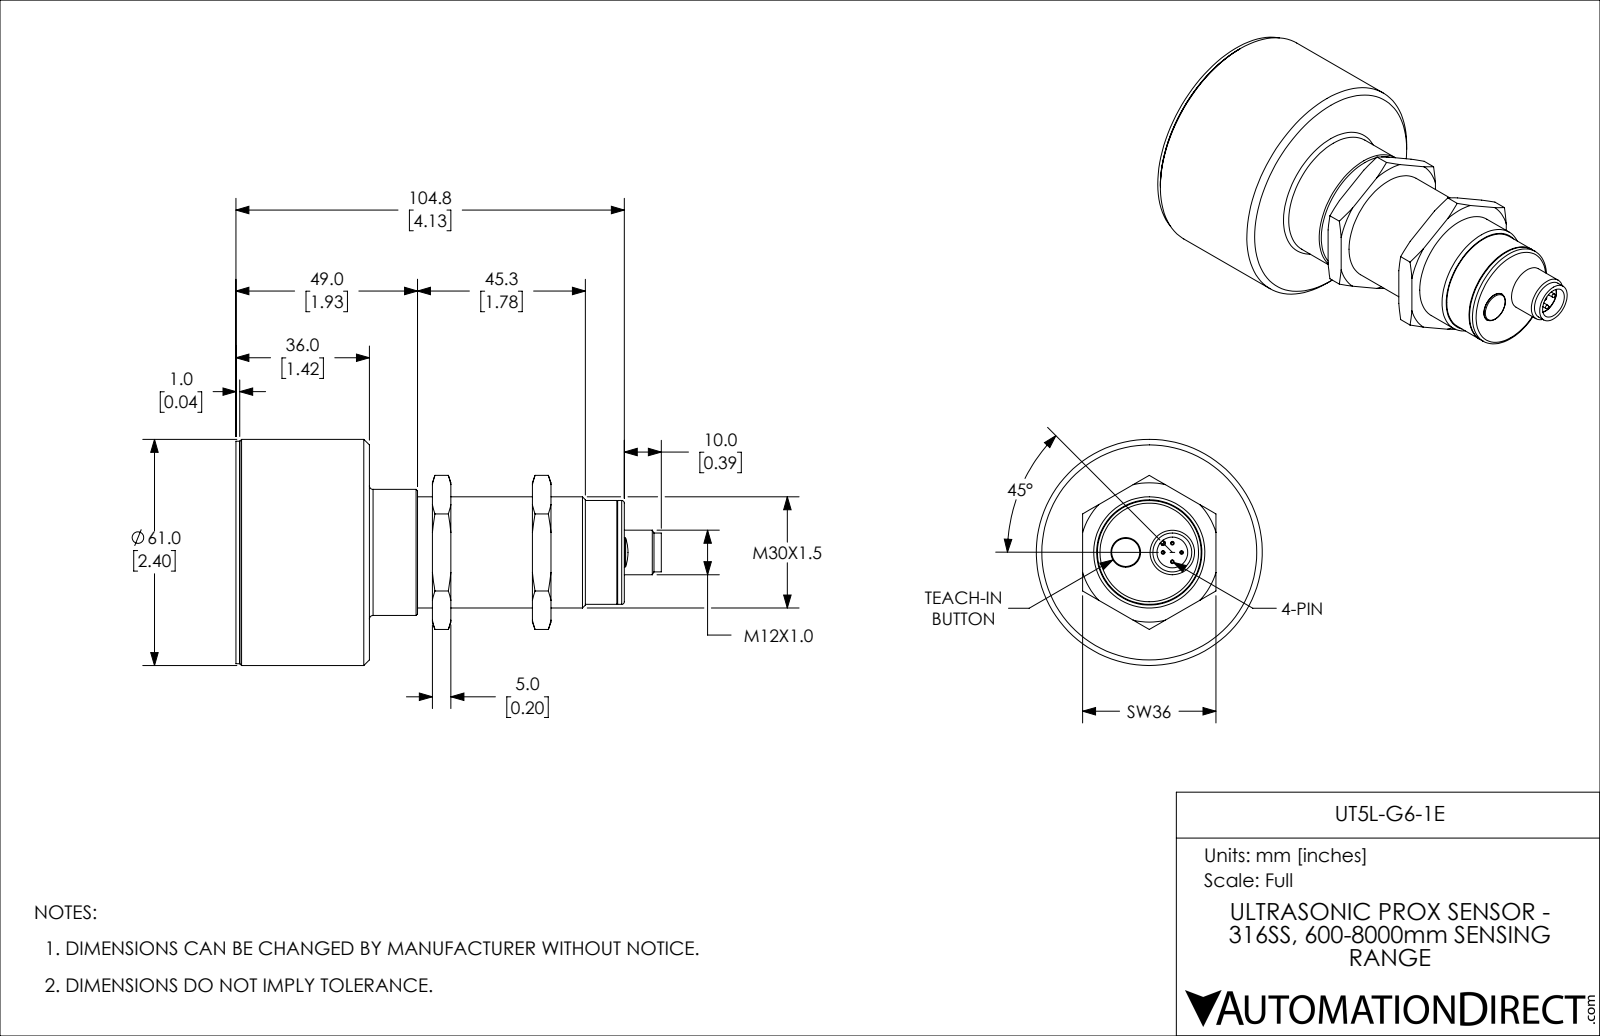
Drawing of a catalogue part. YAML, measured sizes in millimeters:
part_name: "UT5L-G6-1E"
step_written_by: "SolidWorks 2018 (AUTOMOTIVE_DESIGN)"
units: millimeters
bodies: {solids: 9, faces: 180, planar: 52, cylindrical: 57, other: 71}
overall_size: [114.8, 61, 61]
volume: 194457
surface_area: 35986
round_holes:
  - {diameter: 1.8, count: 4}
  - {diameter: 8, count: 1}
  - {diameter: 8.3, count: 1}
  - {diameter: 9.45, count: 1}
  - {diameter: 30, count: 1}
  - {diameter: 50, count: 1}
round_bosses_or_shafts:
  - {diameter: 1, count: 4}
  - {diameter: 61, count: 1}
  - {diameter: 60, count: 1}
  - {diameter: 34, count: 1}
  - {diameter: 28.3, count: 1}
  - {diameter: 28, count: 1}
  - {diameter: 12, count: 1}
  - {diameter: 10.5, count: 1}
partial_cylinders:
  - {radius: 0.3, count: 2}
  - {radius: 0.6, count: 1}
face_to_face_distances: [36, 35, 1, 13, 22, 14, 49, 67, 103, 102]
hole_center_spacings: [2.5, 3.54, 5, 6.71, 12.82, 3.53, 3.72, 6.22]
